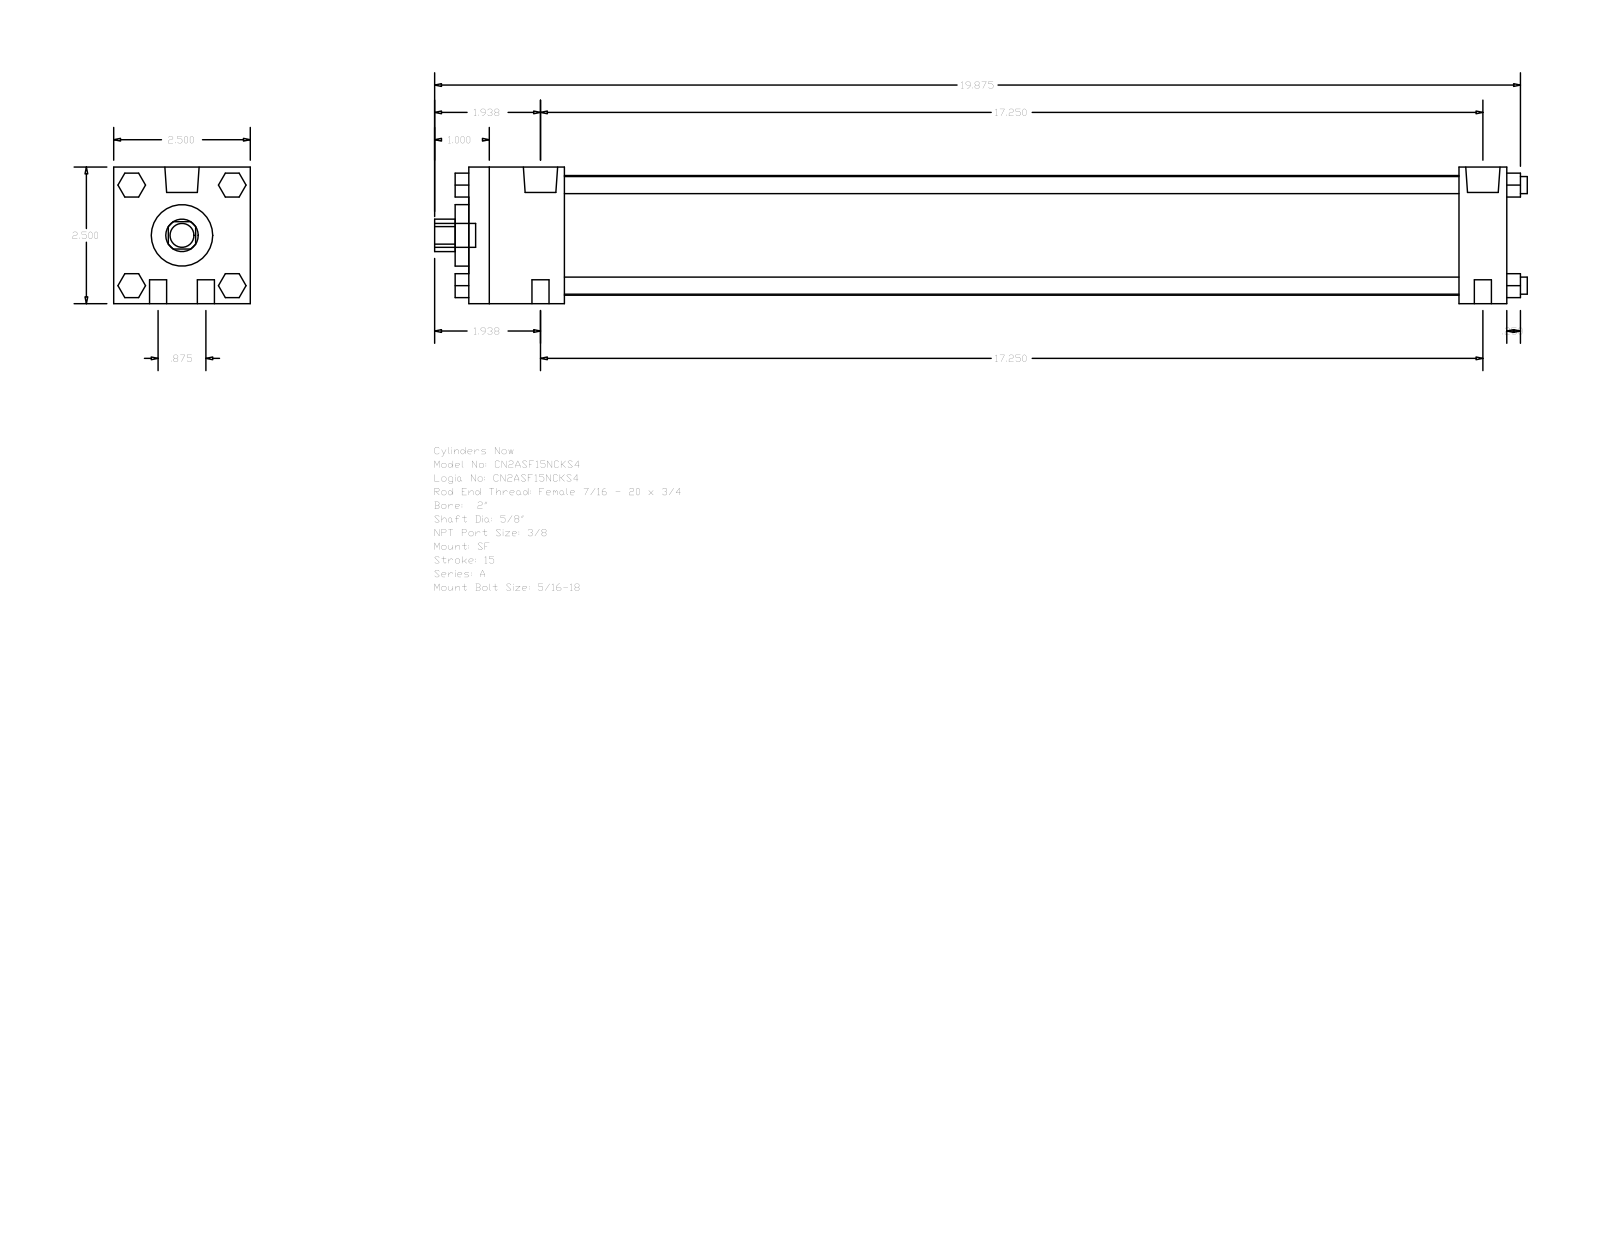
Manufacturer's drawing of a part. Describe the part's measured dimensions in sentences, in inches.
The part is named "A_SF__0200_0.625". Its 3-D file was written by "GSSL Pune (CONFIG_CONTROL_DESIGN)". It is 0 solids with 124 faces: 94 planar, 30 cylindrical and 0 other. Overall it measures 20 by 2.5 by 2.5 inches. Round holes: 1 of diameter 0.625, 1 of diameter 1.125, 1 of diameter 2.19. Round bosses or shafts: 8 of diameter 0.313, 2 of diameter 0.627, 2 of diameter 0.219, 1 of diameter 0.437. Partial cylindrical surfaces (rounded edges, fillets, slot ends): 1 of radius 0.297. The main face-to-face distances are 2.5, 19, 18.125, 0.875, 1.75, 16.375, 17.25, 2, 19.25, 0.25.
